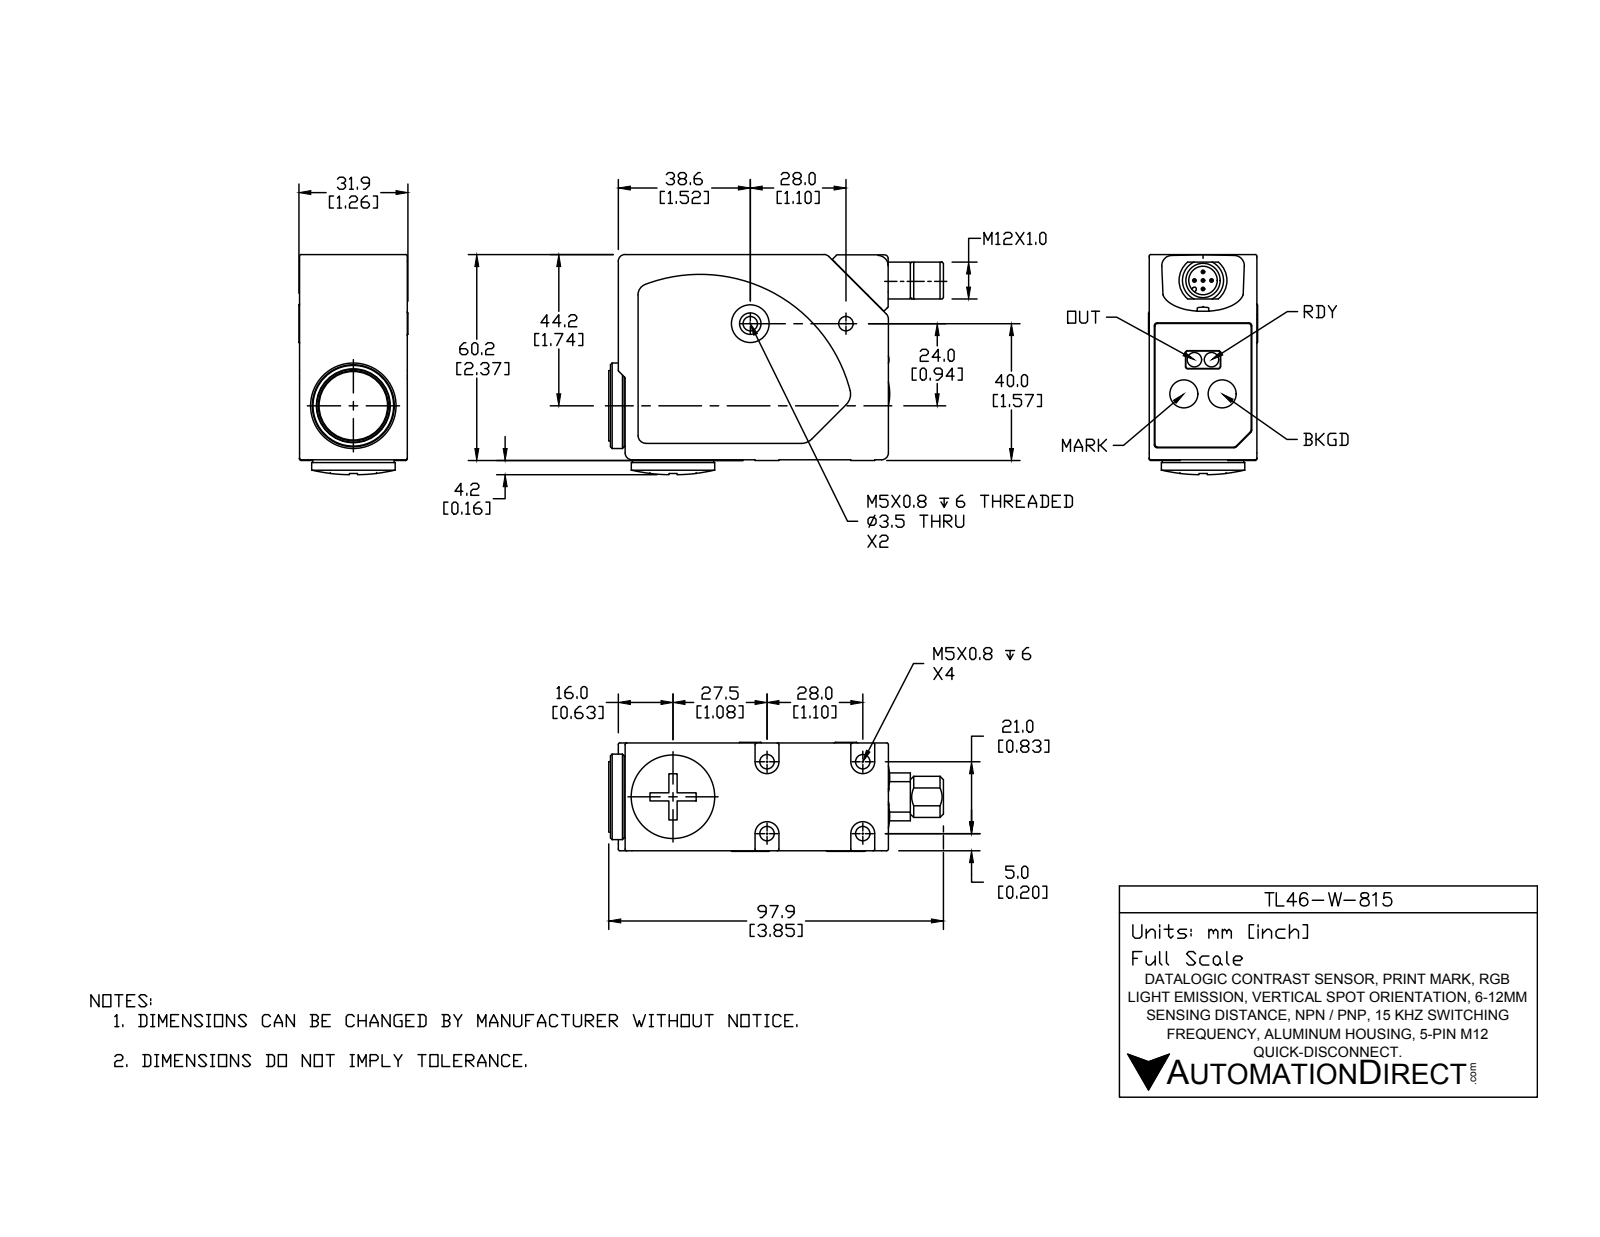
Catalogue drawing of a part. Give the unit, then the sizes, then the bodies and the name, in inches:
Units: inches
Overall size (bounding box): 3.854 × 2.534 × 1.256
Round holes (diameter × count): ⌀0.165 ×8, ⌀0.323 ×2, ⌀0.327 ×1, ⌀0.787 ×1
Round bosses / shafts (diameter × count): ⌀0.039 ×5, ⌀0.937 ×2, ⌀0.984 ×1, ⌀0.961 ×1, ⌀0.748 ×1, ⌀0.433 ×1
Partial cylindrical surfaces — rounded edges, fillets, slot ends (radius × count): R0.02 ×32, R0.031 ×10, R0.024 ×5, R0.079 ×5, R0.02 ×4, R0.138 ×4, R0.236 ×1, R0.276 ×1
Main face-to-face distances: 1.232, 1.224, 1.24, 2.362, 3.11, 3.031, 0.079, 0.016, 1.248, 2.37
Hole centre spacings: 1.102, 0.259, 0.412, 0.507, 0.539, 0.827, 0.917, 1.324
Volume: 9.069 in³ · Surface area: 33.48 in²
Bodies: 7 solids, 332 faces (96 planar, 128 cylindrical, 108 other)
Part name (STEP PRODUCT): TL46-W-815
STEP written by: SolidWorks 2016 (AUTOMOTIVE_DESIGN)
